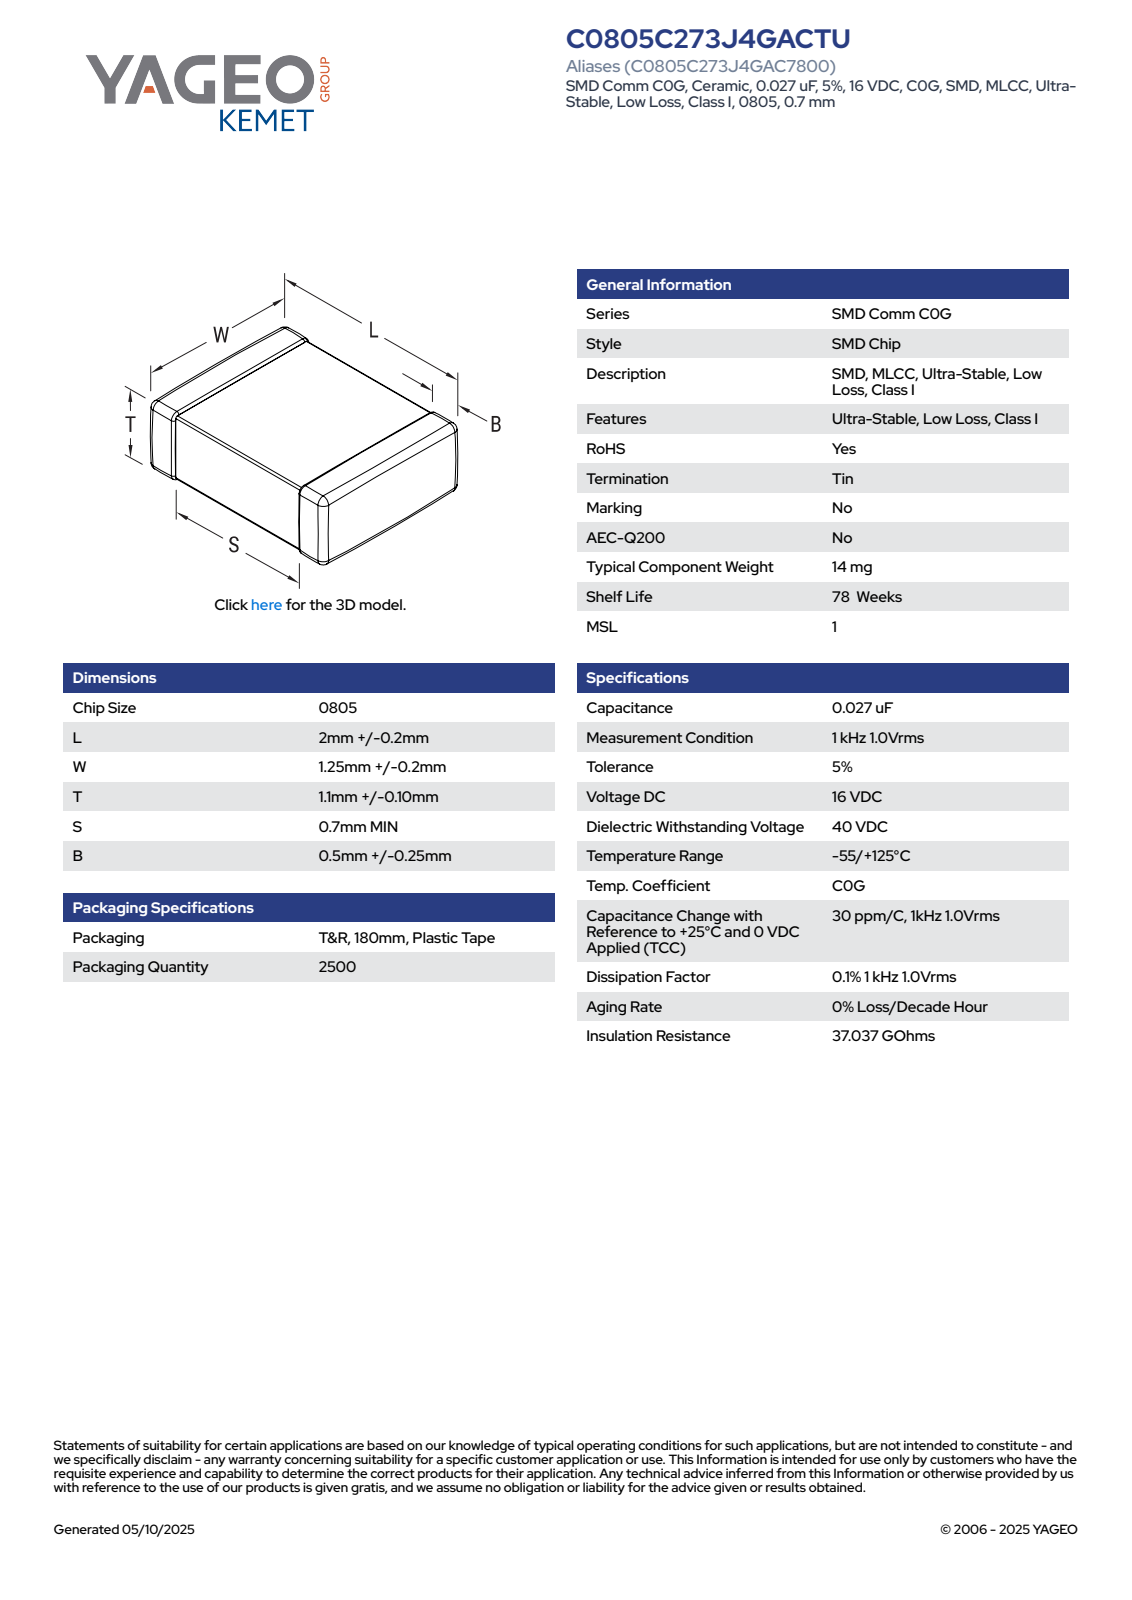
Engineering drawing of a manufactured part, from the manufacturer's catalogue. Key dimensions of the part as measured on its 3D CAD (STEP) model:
Part name (STEP PRODUCT): CCS_CCSTD_0805_L2.2W1.45T1.2B0.5
STEP written by: SolidWorks 2021 (AUTOMOTIVE_DESIGN)
Units: millimetres
Bodies: 4 solids, 125 faces (71 planar, 38 cylindrical, 16 other)
Overall size (bounding box): 2.2 × 1.45 × 1.2
Volume: 4 mm³ · Surface area: 15 mm²
Main face-to-face distances: 1.17, 1.2, 2.2, 1.45, 1.42, 1.14, 1.39, 0.97, 1.23, 1.19
